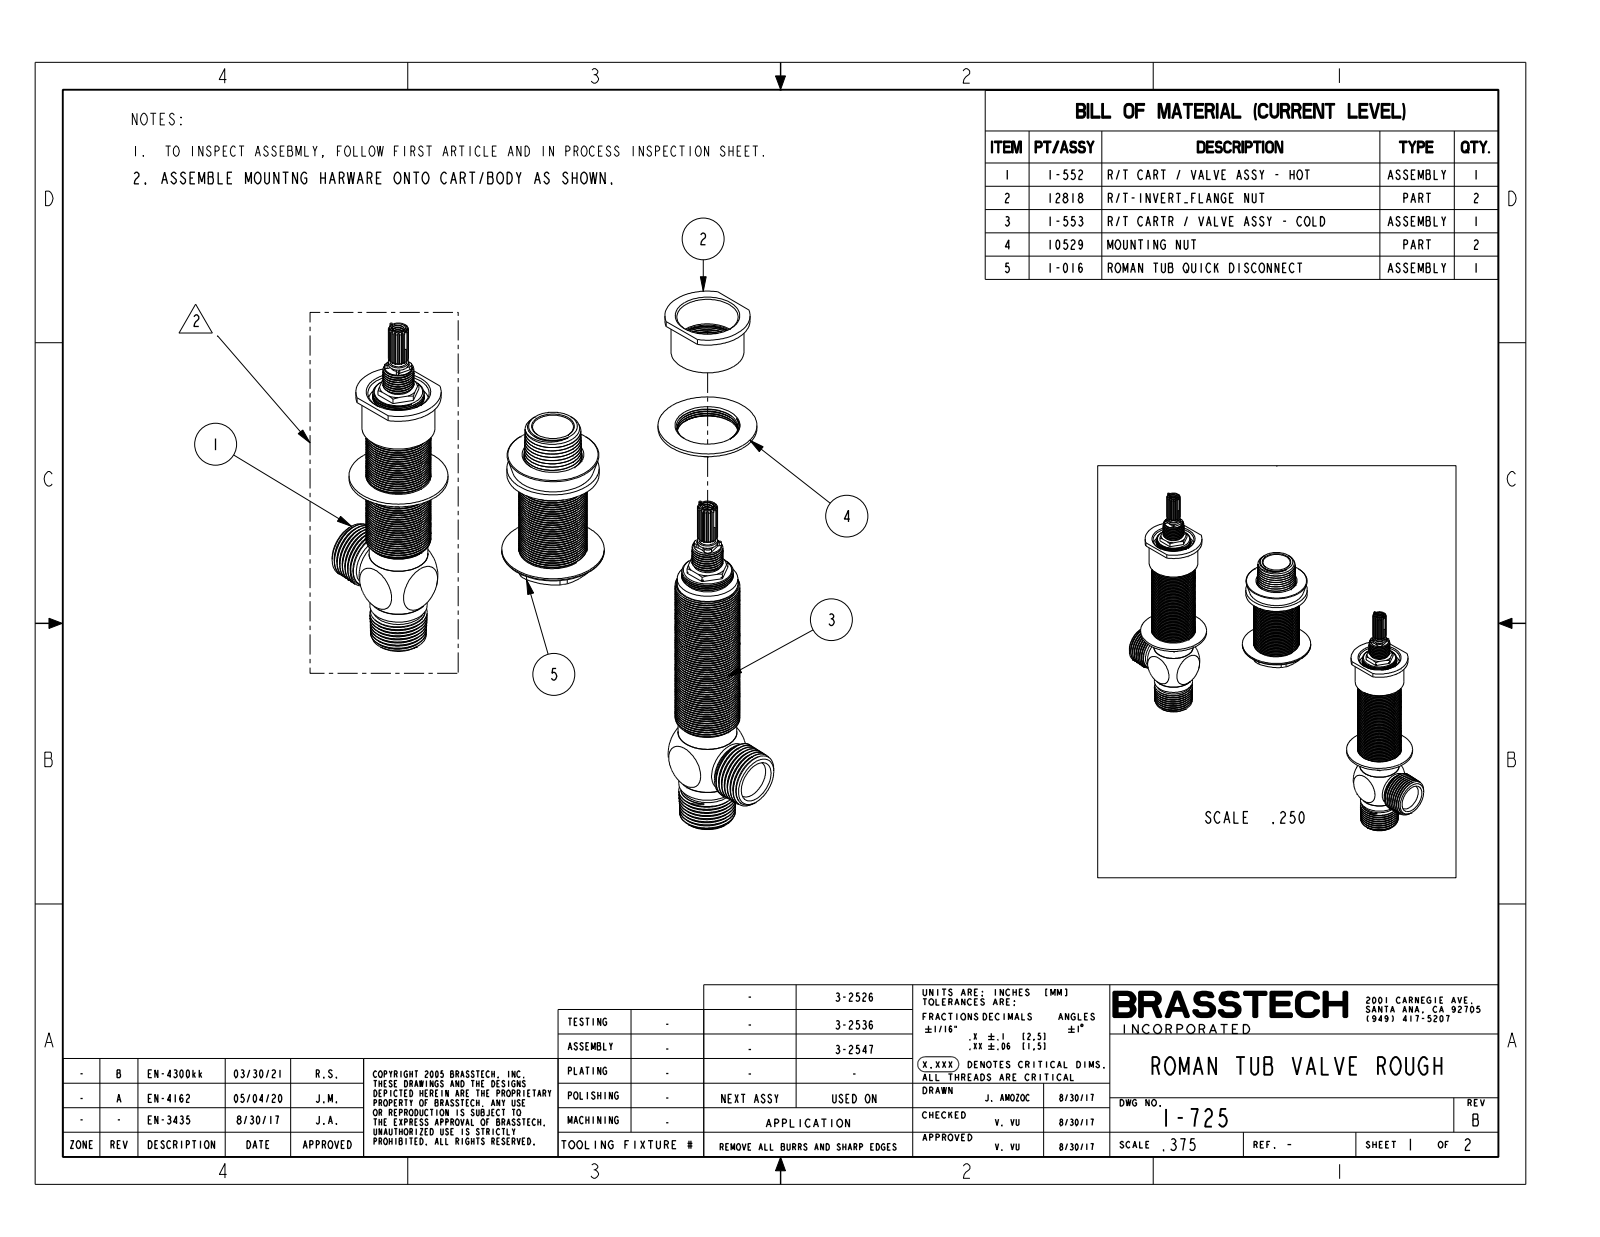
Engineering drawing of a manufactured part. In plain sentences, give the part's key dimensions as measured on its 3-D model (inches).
The part is named "1-725". Its 3-D file was written by "CREO PARAMETRIC BY PTC INC, 2018400 (AUTOMOTIVE_DESIGN)". It is 3 solids with 1163 faces: 226 planar, 493 cylindrical and 444 other. Overall it measures 10.52 by 6.941 by 1.875 inches. Its volume is 17.04 cubic inches and its surface area 119.5 square inches. Round holes: 2 of diameter 0.196, 2 of diameter 0.201, 2 of diameter 1.12, 1 of diameter 0.709, 1 of diameter 1.18. Round bosses or shafts: 2 of diameter 1.811, 2 of diameter 1.335, 2 of diameter 1.187, 2 of diameter 1.11, 2 of diameter 1.075, 2 of diameter 1.047, 2 of diameter 0.945, 2 of diameter 0.929. Partial cylindrical surfaces (rounded edges, fillets, slot ends): 8 of radius 0.04, 8 of radius 0.08, 2 of radius 0.164, 2 of radius 0.26, 2 of radius 0.3, 2 of radius 0.775, 2 of radius 0.781, 1 of radius 0.758. The main face-to-face distances are 0.061, 3.15, 3.089, 1.616, 1.555, 1.534, 1.337, 1.424, 3.742, 3.681. The hole center spacings are 8.
